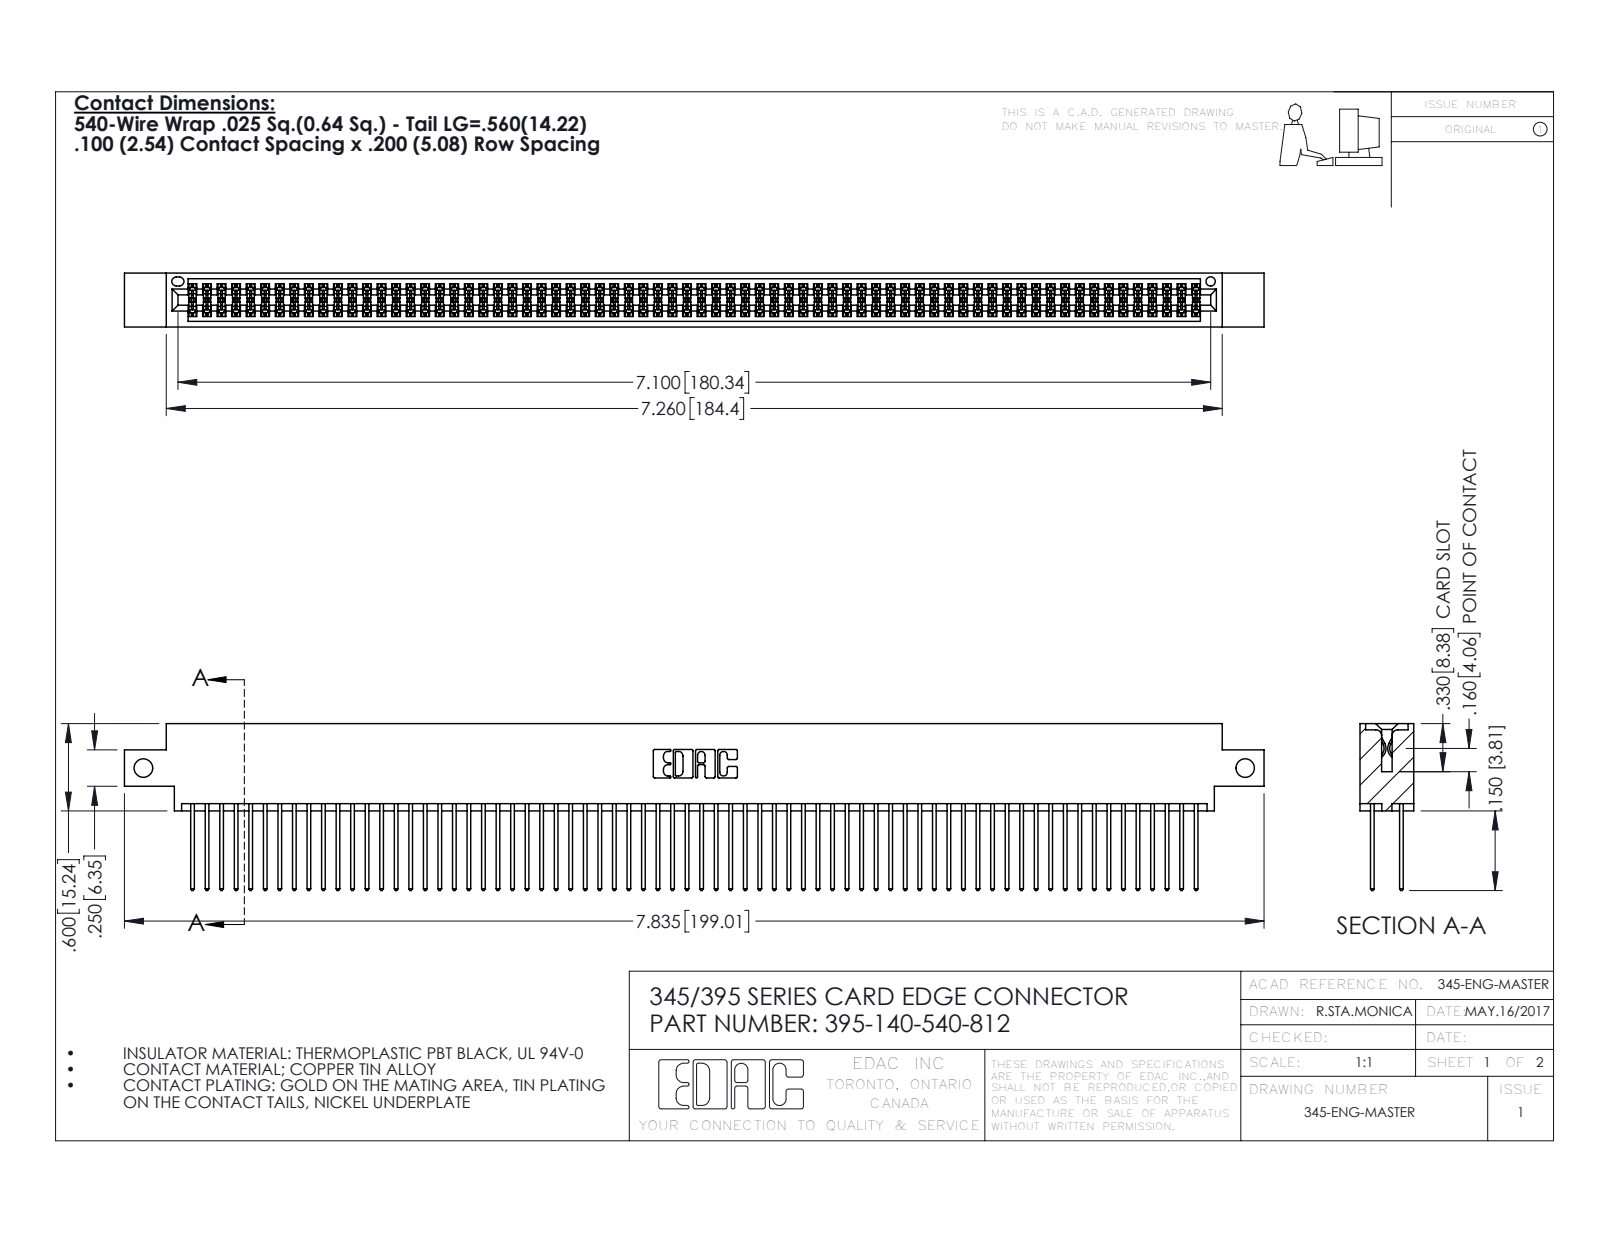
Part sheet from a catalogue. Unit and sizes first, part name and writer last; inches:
Units: inches
Overall size (bounding box): 7.835 × 1.147 × 0.37
Round holes (diameter × count): ⌀0.128 ×2, ⌀0.064 ×1
Partial cylindrical surfaces — rounded edges, fillets, slot ends (radius × count): R0.006 ×210, R0.01 ×140, R0.01 ×22, R0.007 ×6, R0.031 ×6, R0.026 ×3, R0.014 ×2, R0.019 ×2
Main face-to-face distances: 0.072, 0.298, 0.2, 0.098, 0.272, 0.025, 0.37, 0.225, 0.175, 0.149
Hole centre spacings: 7.575
Volume: 1.216 in³ · Surface area: 50.31 in²
Bodies: 141 solids, 7130 faces (4704 planar, 2426 cylindrical, 0 other)
Part name (STEP PRODUCT): 395-140-540-812; 345-292-001_345-293-140; 345 Part_0.170 Offset - Side Mount
STEP written by: SolidWorks 2016 (CONFIG_CONTROL_DESIGN)
